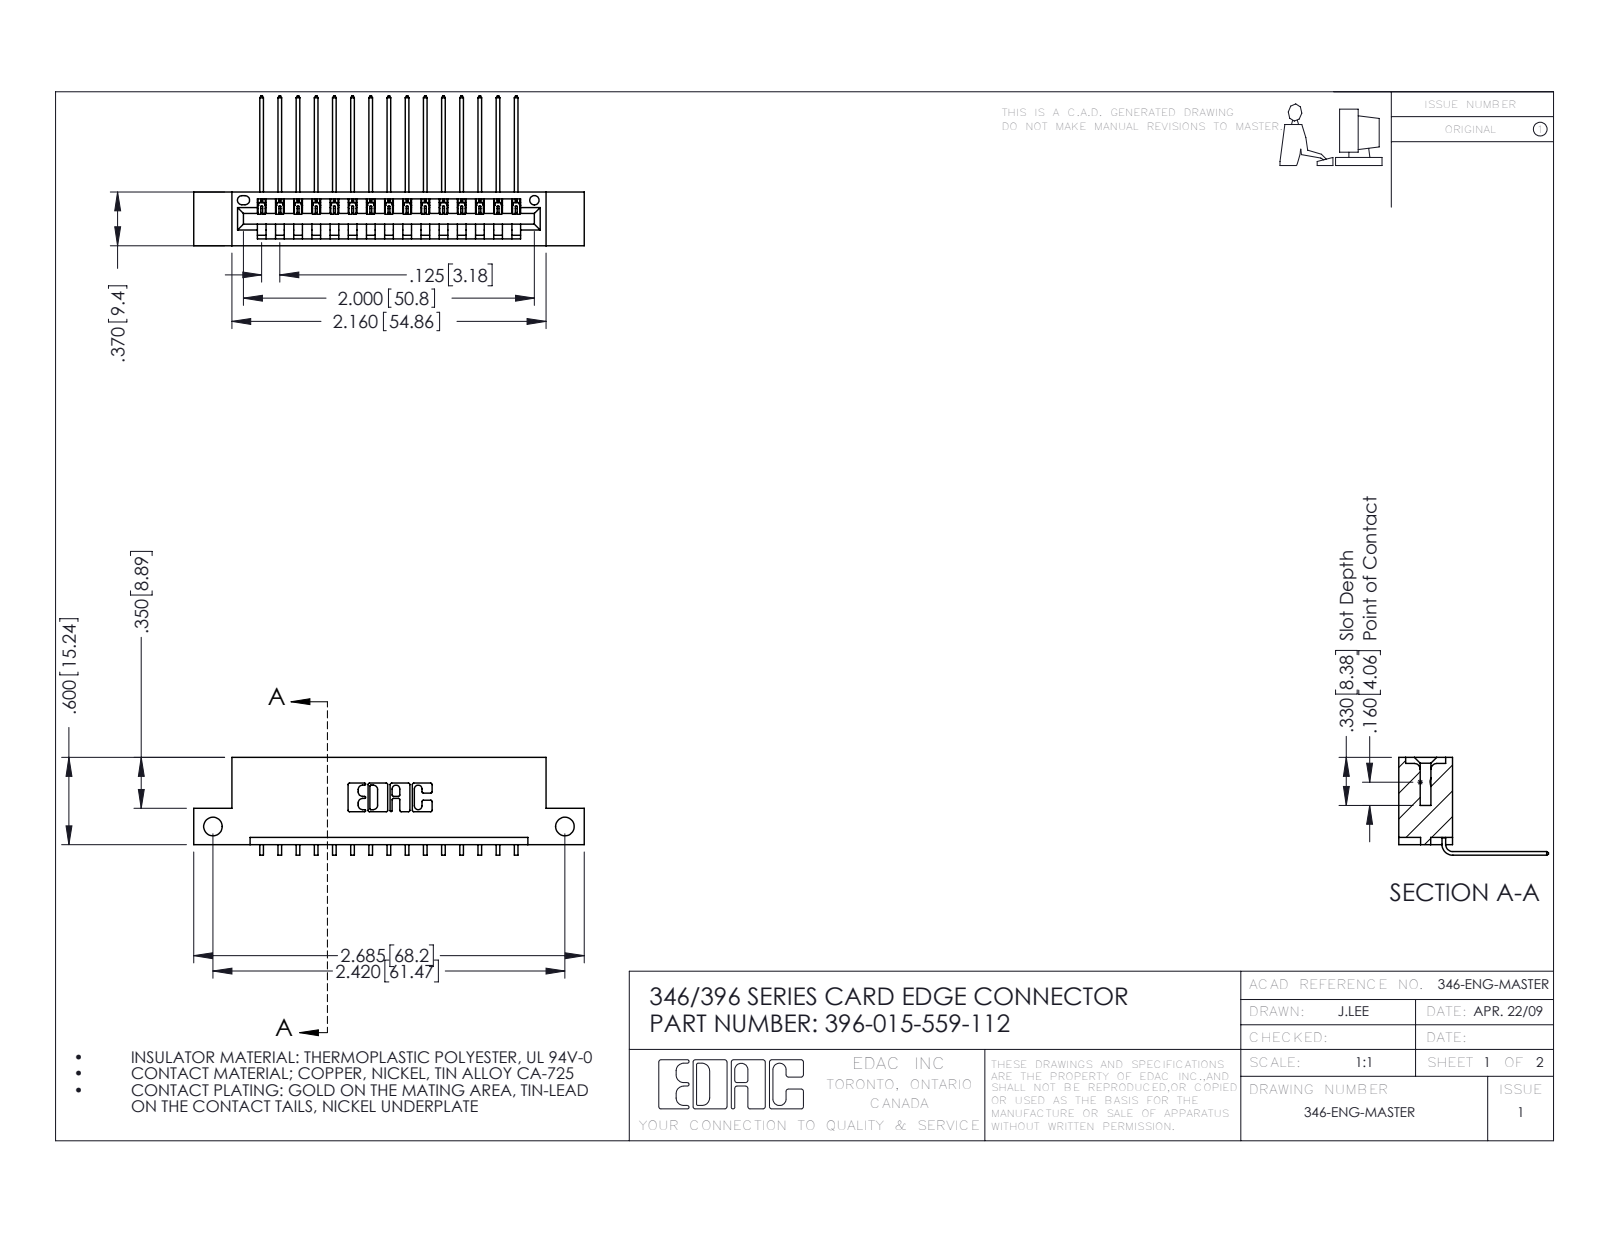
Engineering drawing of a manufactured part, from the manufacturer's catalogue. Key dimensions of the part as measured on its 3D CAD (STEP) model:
Part name (STEP PRODUCT): 346 Part_Flush Mounting Lugs - Side Mount; 345-292-001_558 559 Tail - 1; 396-015-559-112
STEP written by: SolidWorks 2016 (CONFIG_CONTROL_DESIGN)
Units: inches
Bodies: 16 solids, 1022 faces (706 planar, 316 cylindrical, 0 other)
Overall size (bounding box): 2.685 × 1.03 × 0.673
Volume: 0.385 in³ · Surface area: 12 in²
Round holes (diameter × count): ⌀0.128 ×2, ⌀0.064 ×1
Partial cylindrical surfaces — rounded edges, fillets, slot ends (radius × count): R0.006 ×30, R0.01 ×22, R0.007 ×6, R0.031 ×6, R0.026 ×3, R0.031 ×2, R0.04 ×2, R0.014 ×1
Main face-to-face distances: 0.048, 0.322, 0.25, 0.37, 0.072, 0.025, 0.298, 0.148, 0.222, 0.1
Hole centre spacings: 2.42
